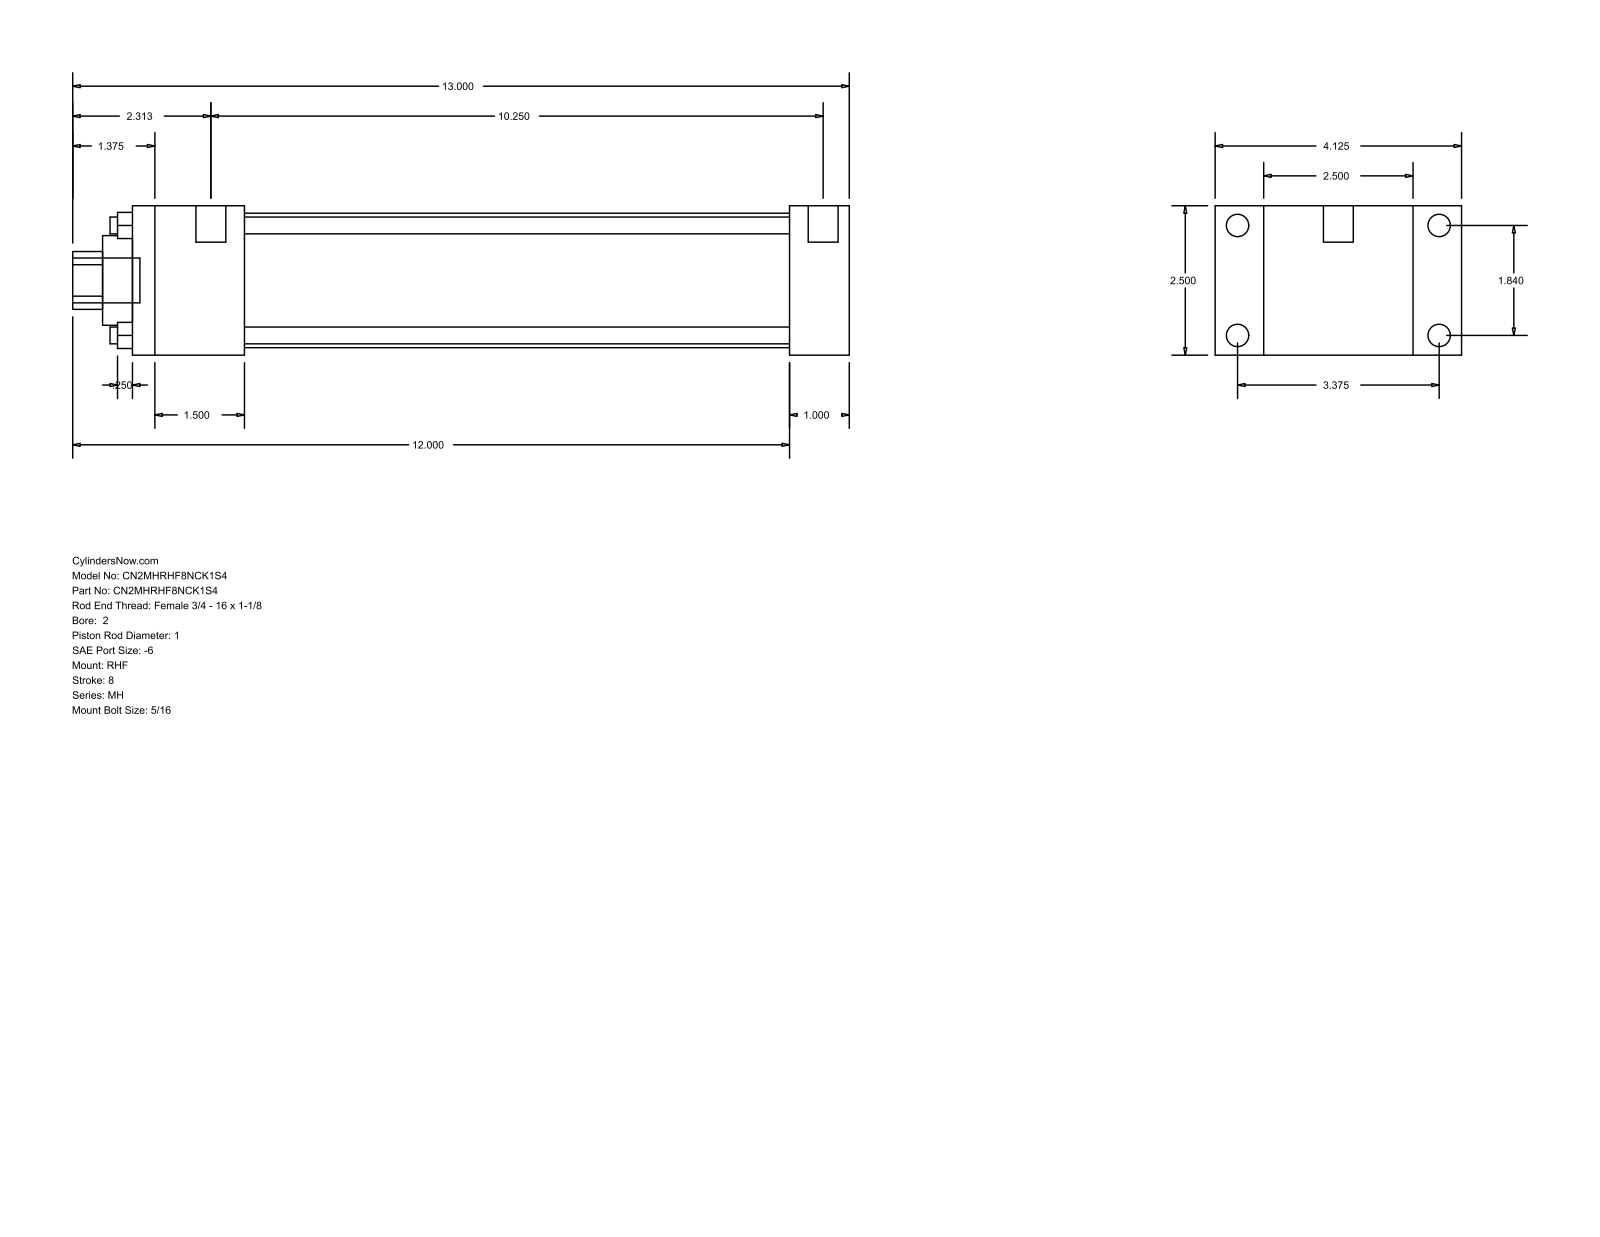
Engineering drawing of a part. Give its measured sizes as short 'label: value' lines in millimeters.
name: MH_RHF__0200_1
written by: GSSL Pune (CONFIG_CONTROL_DESIGN)
unit: mm
bodies: 0 solids, 88 faces (60 planar, 28 cylindrical, 0 other)
size: 330.2 × 104.78 × 63.5
holes: 4× ⌀7.14, 1× ⌀25.4, 1× ⌀38.1, 1× ⌀57.15
bosses: 4× ⌀9.53, 4× ⌀5.56, 2× ⌀12.7, 1× ⌀19.05
rounds: 1× R12.29
face distances: 63.5, 25.4, 20.64, 84.14, 304.8, 279.4, 104.78, 47.63, 231.77, 257.17
hole spacings: 33.05, 46.74, 66.1
